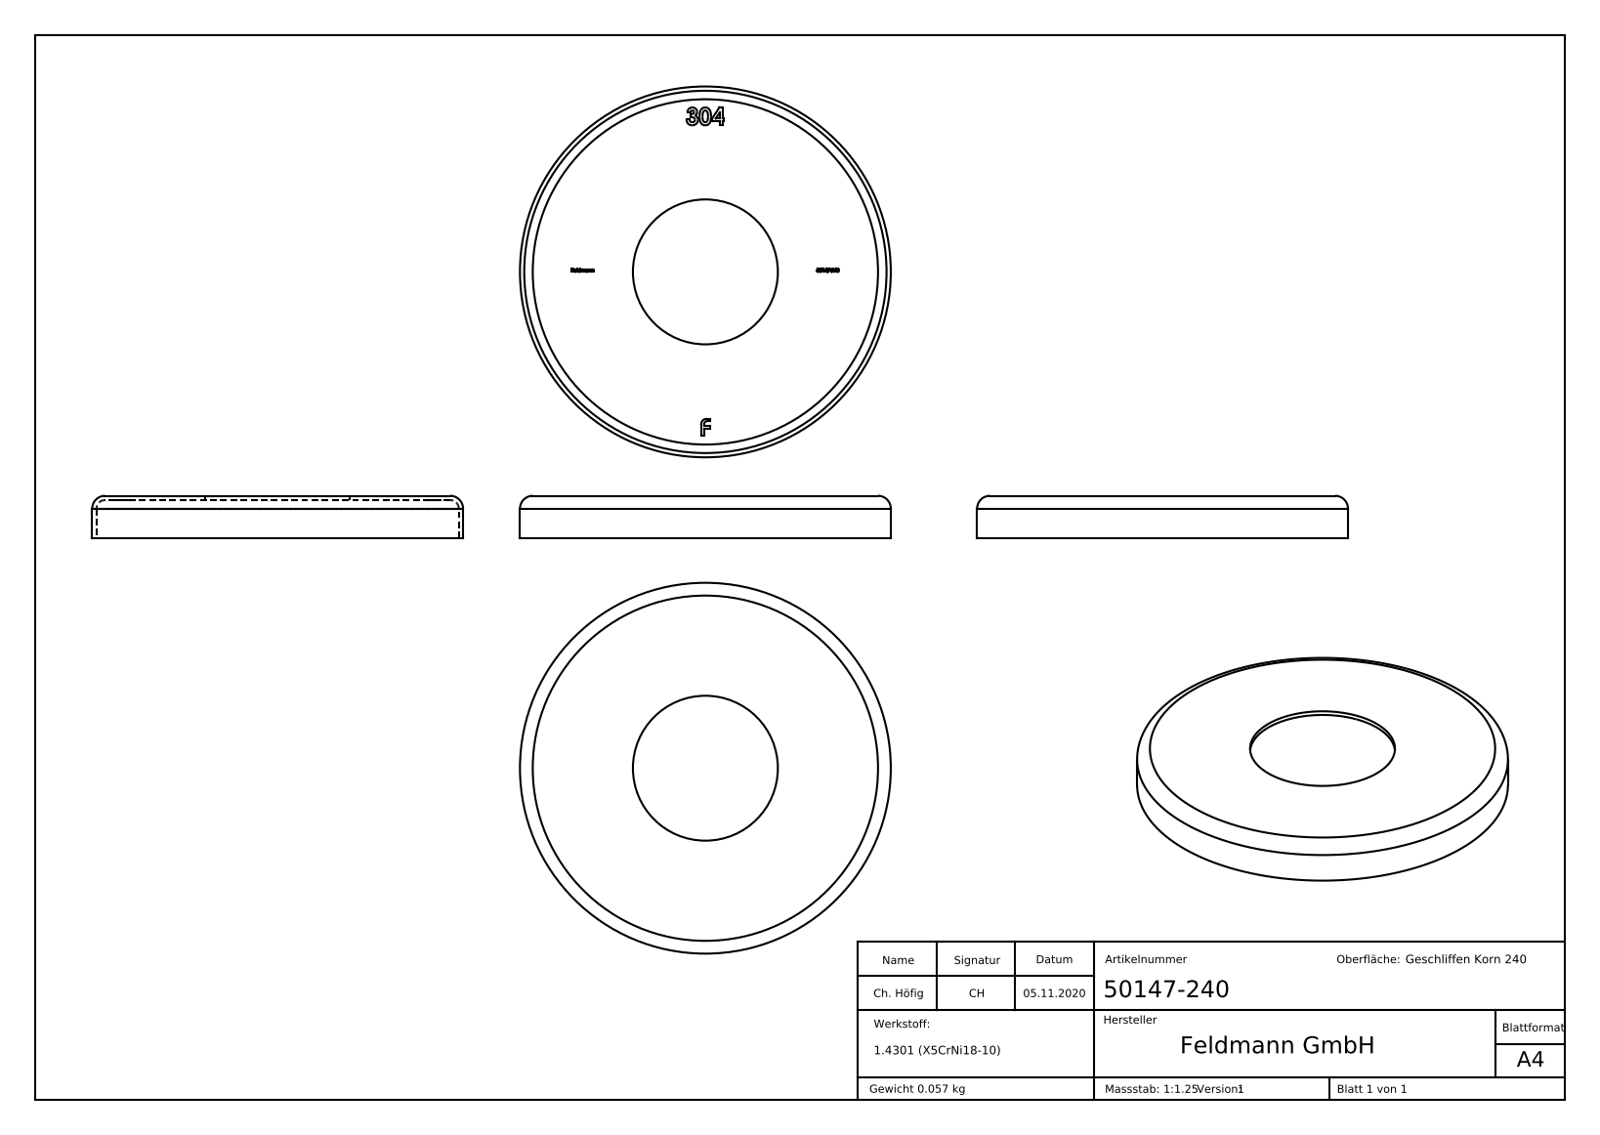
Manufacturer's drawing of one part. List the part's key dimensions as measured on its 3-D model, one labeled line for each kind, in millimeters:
Part name (STEP PRODUCT): 50147-240
STEP written by: SolidWorks 2018 (CONFIG_CONTROL_DESIGN)
Units: millimetres
Bodies: 1 solid, 283 faces (168 planar, 6 cylindrical, 109 other)
Overall size (bounding box): 87 × 87 × 10
Volume: 7 173 mm³ · Surface area: 14 742 mm²
Round holes (diameter × count): ⌀34 ×1, ⌀85 ×1
Round bosses / shafts (diameter × count): ⌀87 ×1
Main face-to-face distances: 1, 9, 10, 9.1, 0.9, 0.71, 5, 35.27, 4.29, 0.58
